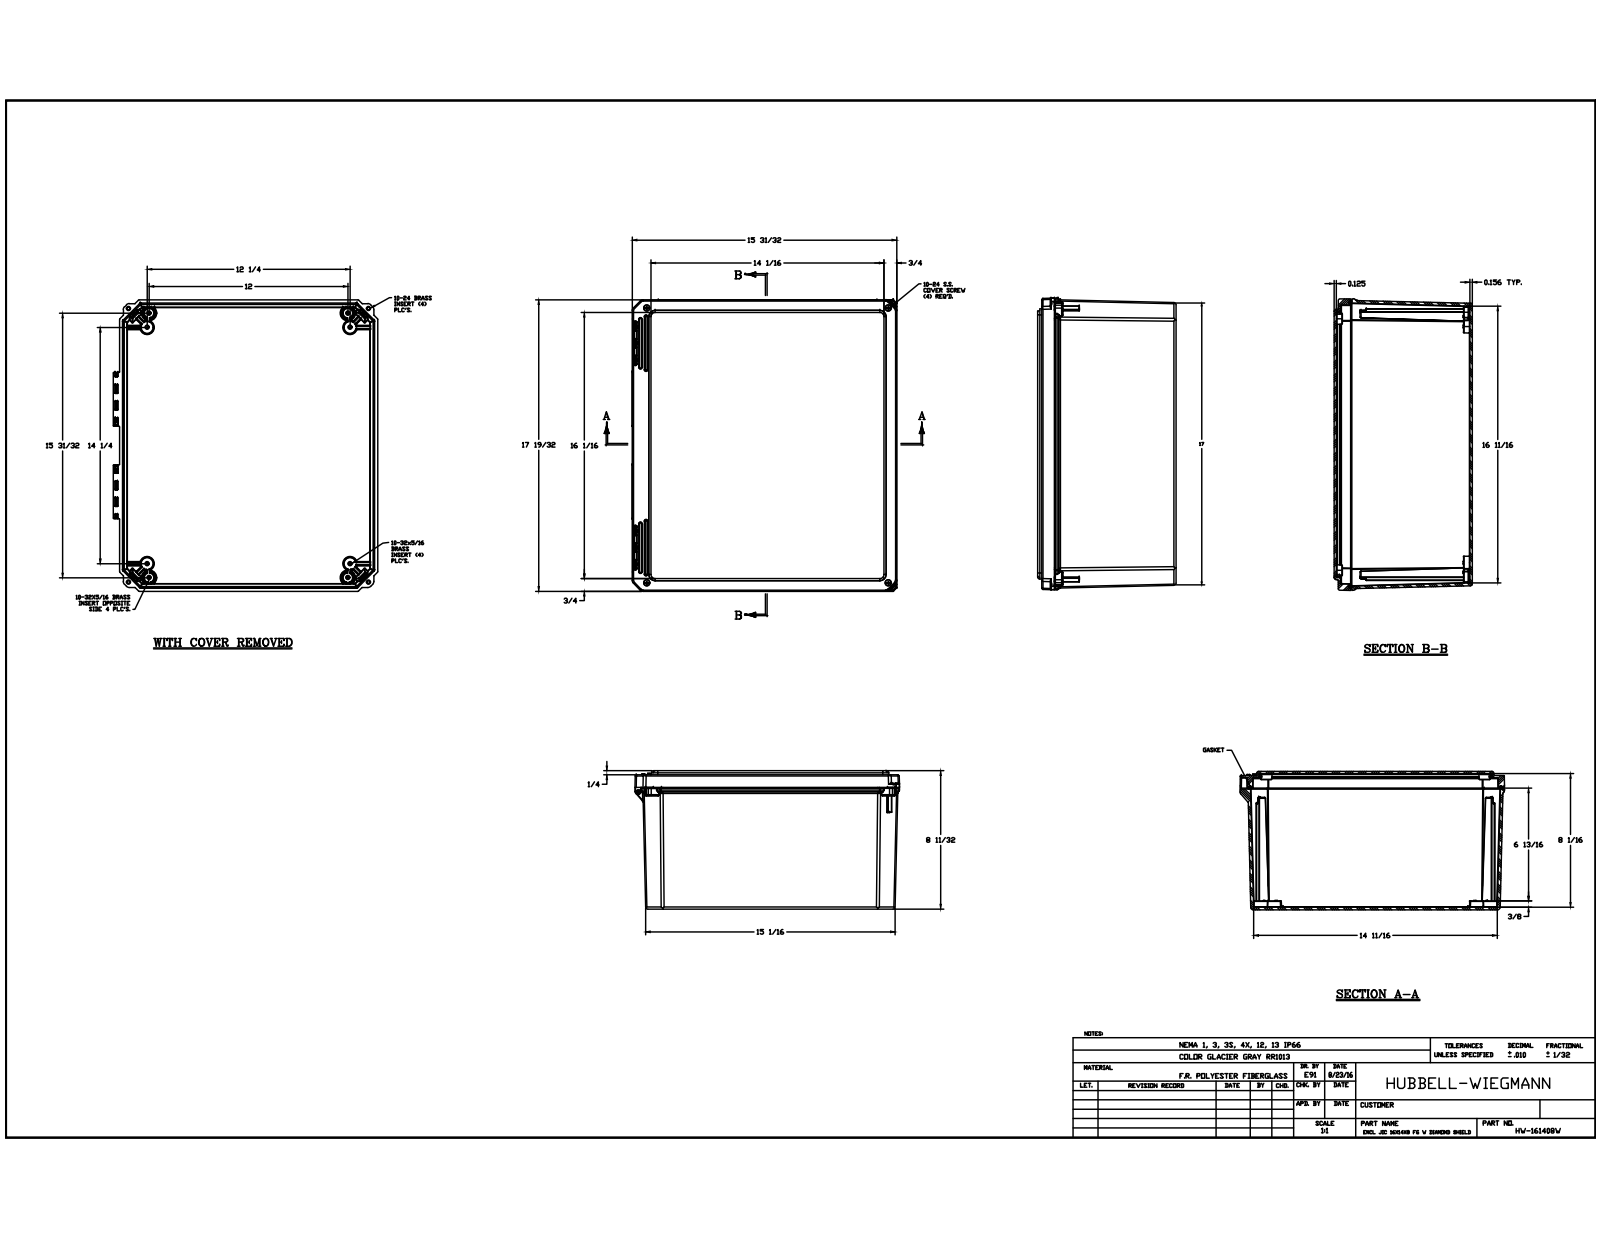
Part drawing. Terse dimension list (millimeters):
name: HW-161408SC; DS161408BOX; BRASS INSERT-(; BRASS INSERT-(_1 (+6 more)
written by: Autodesk Inventor 2017 (CONFIG_CONTROL_DESIGN)
unit: mm
bodies: 27 solids, 2157 faces (729 planar, 786 cylindrical, 642 other)
size: 447.08 × 405.44 × 211.87
volume: 3 017 000 mm³; area: 1 432 000 mm²
holes: 16× ⌀3.96, 8× ⌀3.86, 4× ⌀6.4, 4× ⌀6.43, 2× ⌀5.56, 2× ⌀5.77, 2× ⌀7.94, 1× ⌀3.48
bosses: 16× ⌀6.25, 4× ⌀11.43, 4× ⌀5.05, 1× ⌀11.05, 1× ⌀11.05
rounds: 175× R0.25, 80× R0.13, 57× R0.51, 45× R0.76, 26× R1.59, 24× R0.76, 24× R2.29, 24× R2.44
face distances: 3.17, 3.96, 207.91, 211.87, 208.7, 204.74, 4.56, 4.59, 6.35, 9.52
hole spacings: 337.73, 342.1, 21.98, 33.78, 41.95, 308.74, 383.7, 392.71
